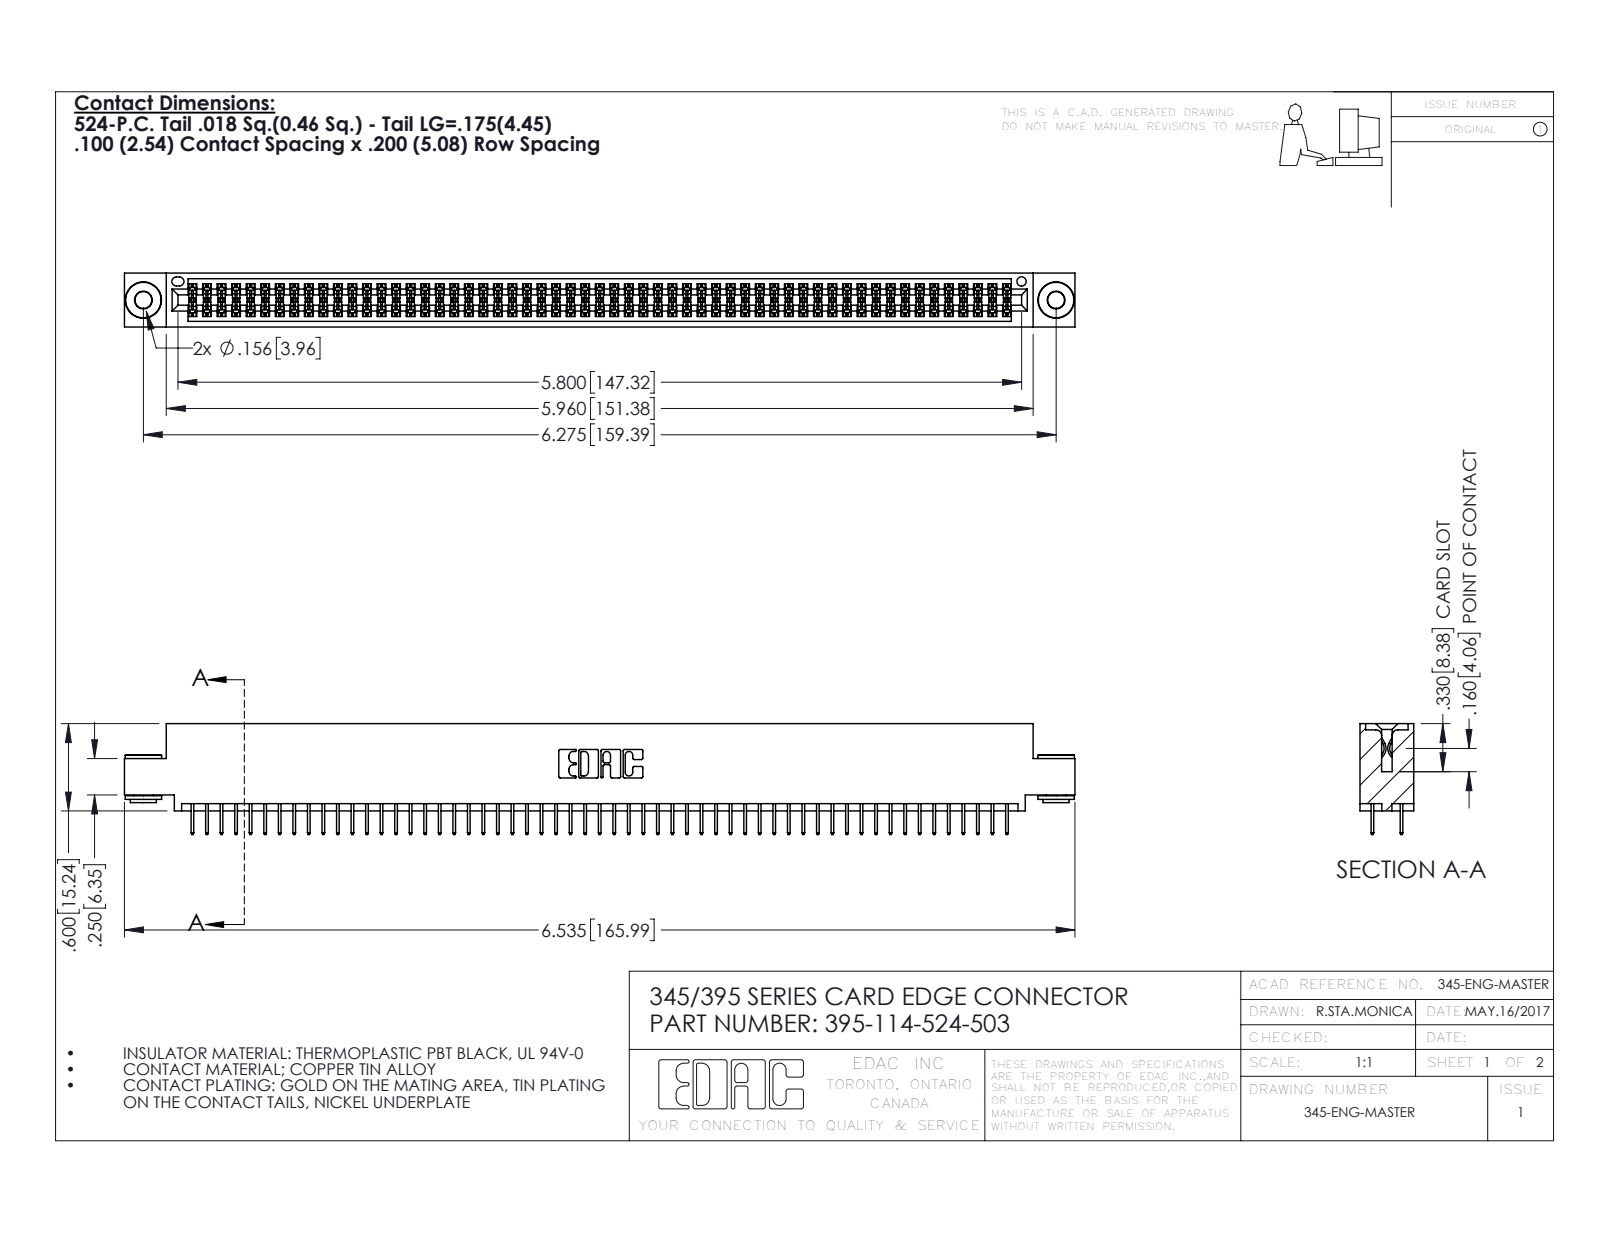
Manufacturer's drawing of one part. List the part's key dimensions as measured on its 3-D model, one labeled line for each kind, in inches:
Part name (STEP PRODUCT): 345-292-001_345-293-124; 395-114-524-503; 345 Part_0.110 Offset - 0.156 Dia-TH; 345-250-002_345-250-002-102
STEP written by: SolidWorks 2016 (CONFIG_CONTROL_DESIGN)
Units: inches
Bodies: 117 solids, 6324 faces (4540 planar, 1776 cylindrical, 8 other)
Overall size (bounding box): 6.535 × 0.762 × 0.37
Volume: 0.979 in³ · Surface area: 36.95 in²
Round holes (diameter × count): ⌀0.116 ×2, ⌀0.156 ×2, ⌀0.064 ×1
Round bosses / shafts (diameter × count): ⌀0.25 ×2, ⌀0.18 ×2, ⌀0.136 ×2
Partial cylindrical surfaces — rounded edges, fillets, slot ends (radius × count): R0.006 ×171, R0.01 ×22, R0.007 ×6, R0.031 ×6, R0.026 ×3, R0.014 ×2, R0.019 ×2, R0.022 ×2
Main face-to-face distances: 0.072, 0.298, 0.2, 0.37, 0.025, 0.098, 0.272, 0.225, 0.072, 0.175
Hole centre spacings: 0.27, 6.039, 6.275
